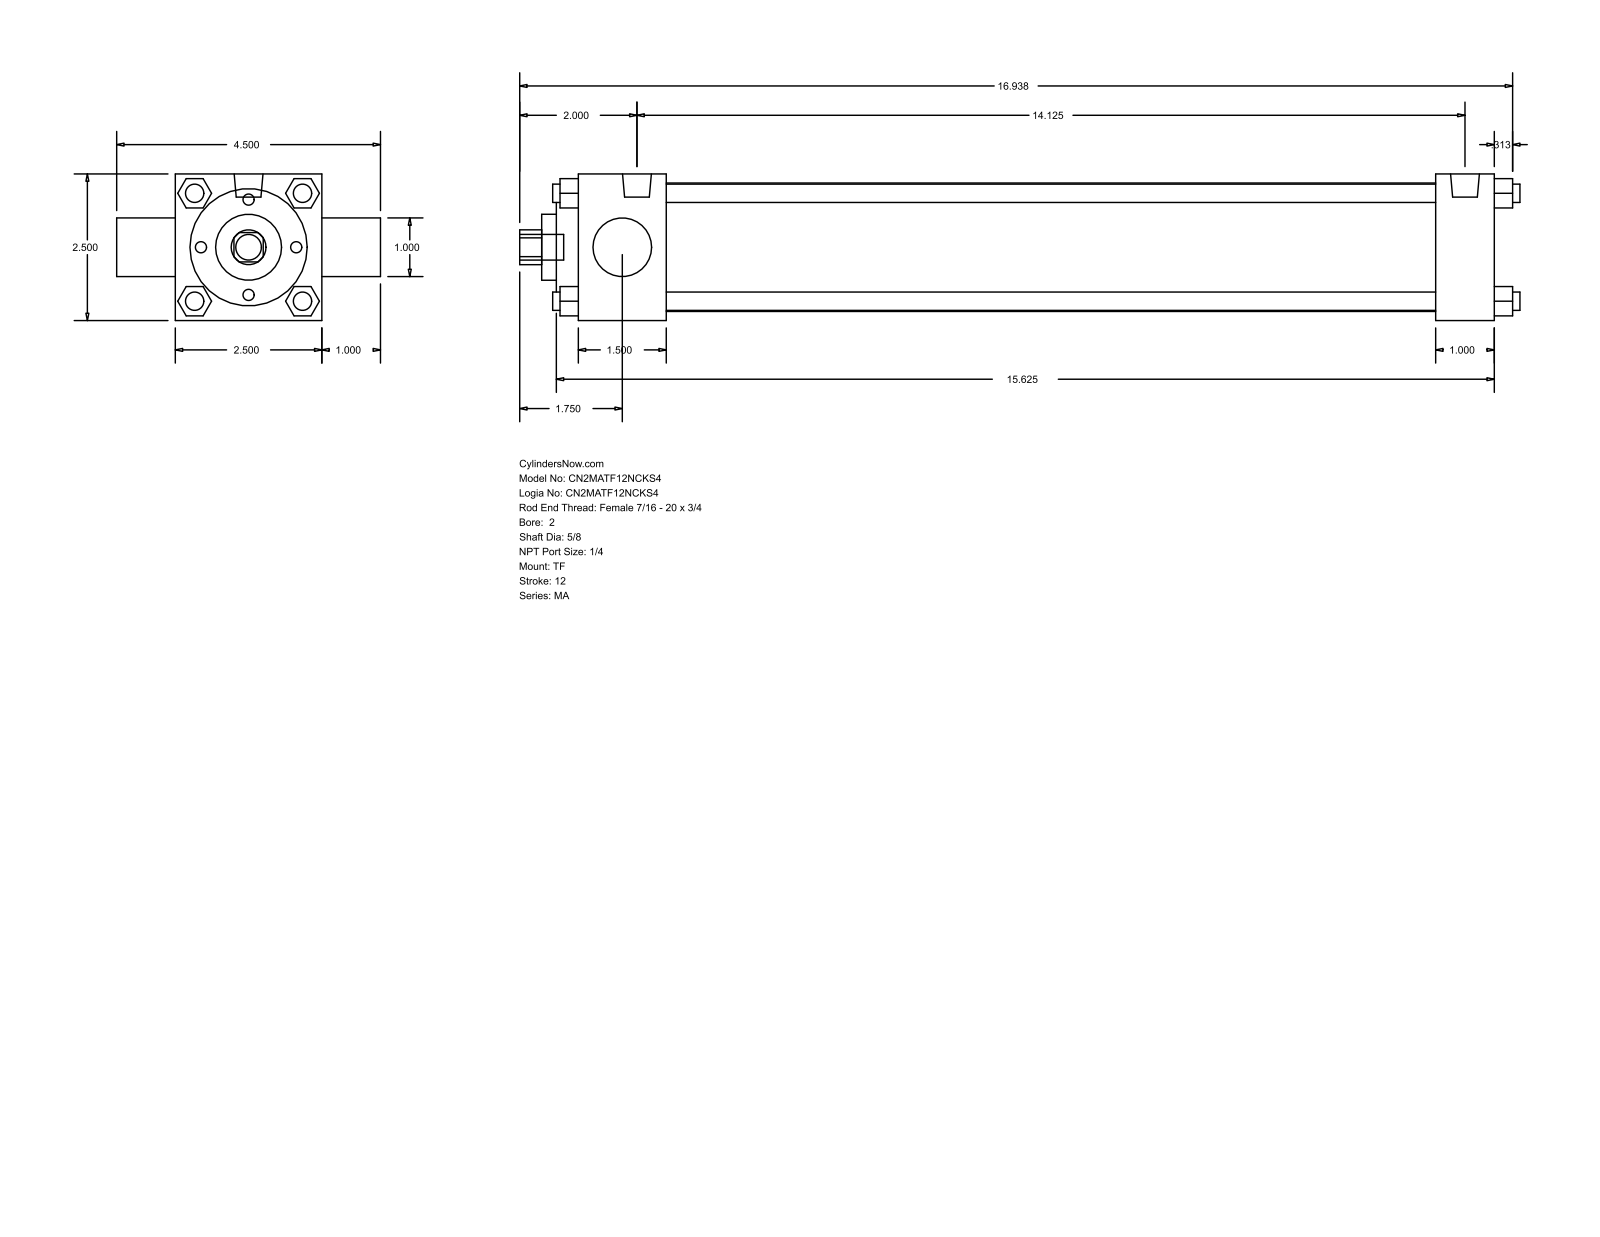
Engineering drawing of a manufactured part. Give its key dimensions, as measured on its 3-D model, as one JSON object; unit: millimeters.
{"part_name": "MA_TF__0200_0.625", "step_written_by": "GSSL Pune (CONFIG_CONTROL_DESIGN)", "units": "millimeters", "bodies": {"solids": 0, "faces": 122, "planar": 93, "cylindrical": 29, "other": 0}, "overall_size": [433.39, 114.3, 63.5], "round_holes": [[15.88, 1], [25.4, 1], [28.57, 1], [50.8, 1], [55.63, 1]], "round_bosses_or_shafts": [[7.94, 7], [12.49, 2], [11.11, 1]], "partial_cylinders_radius": [[7.54, 1]], "face_to_face_distances": [63.5, 38.1, 12.7, 9.52, 396.87, 371.48, 333.38, 358.77, 25.39, 47.62]}
